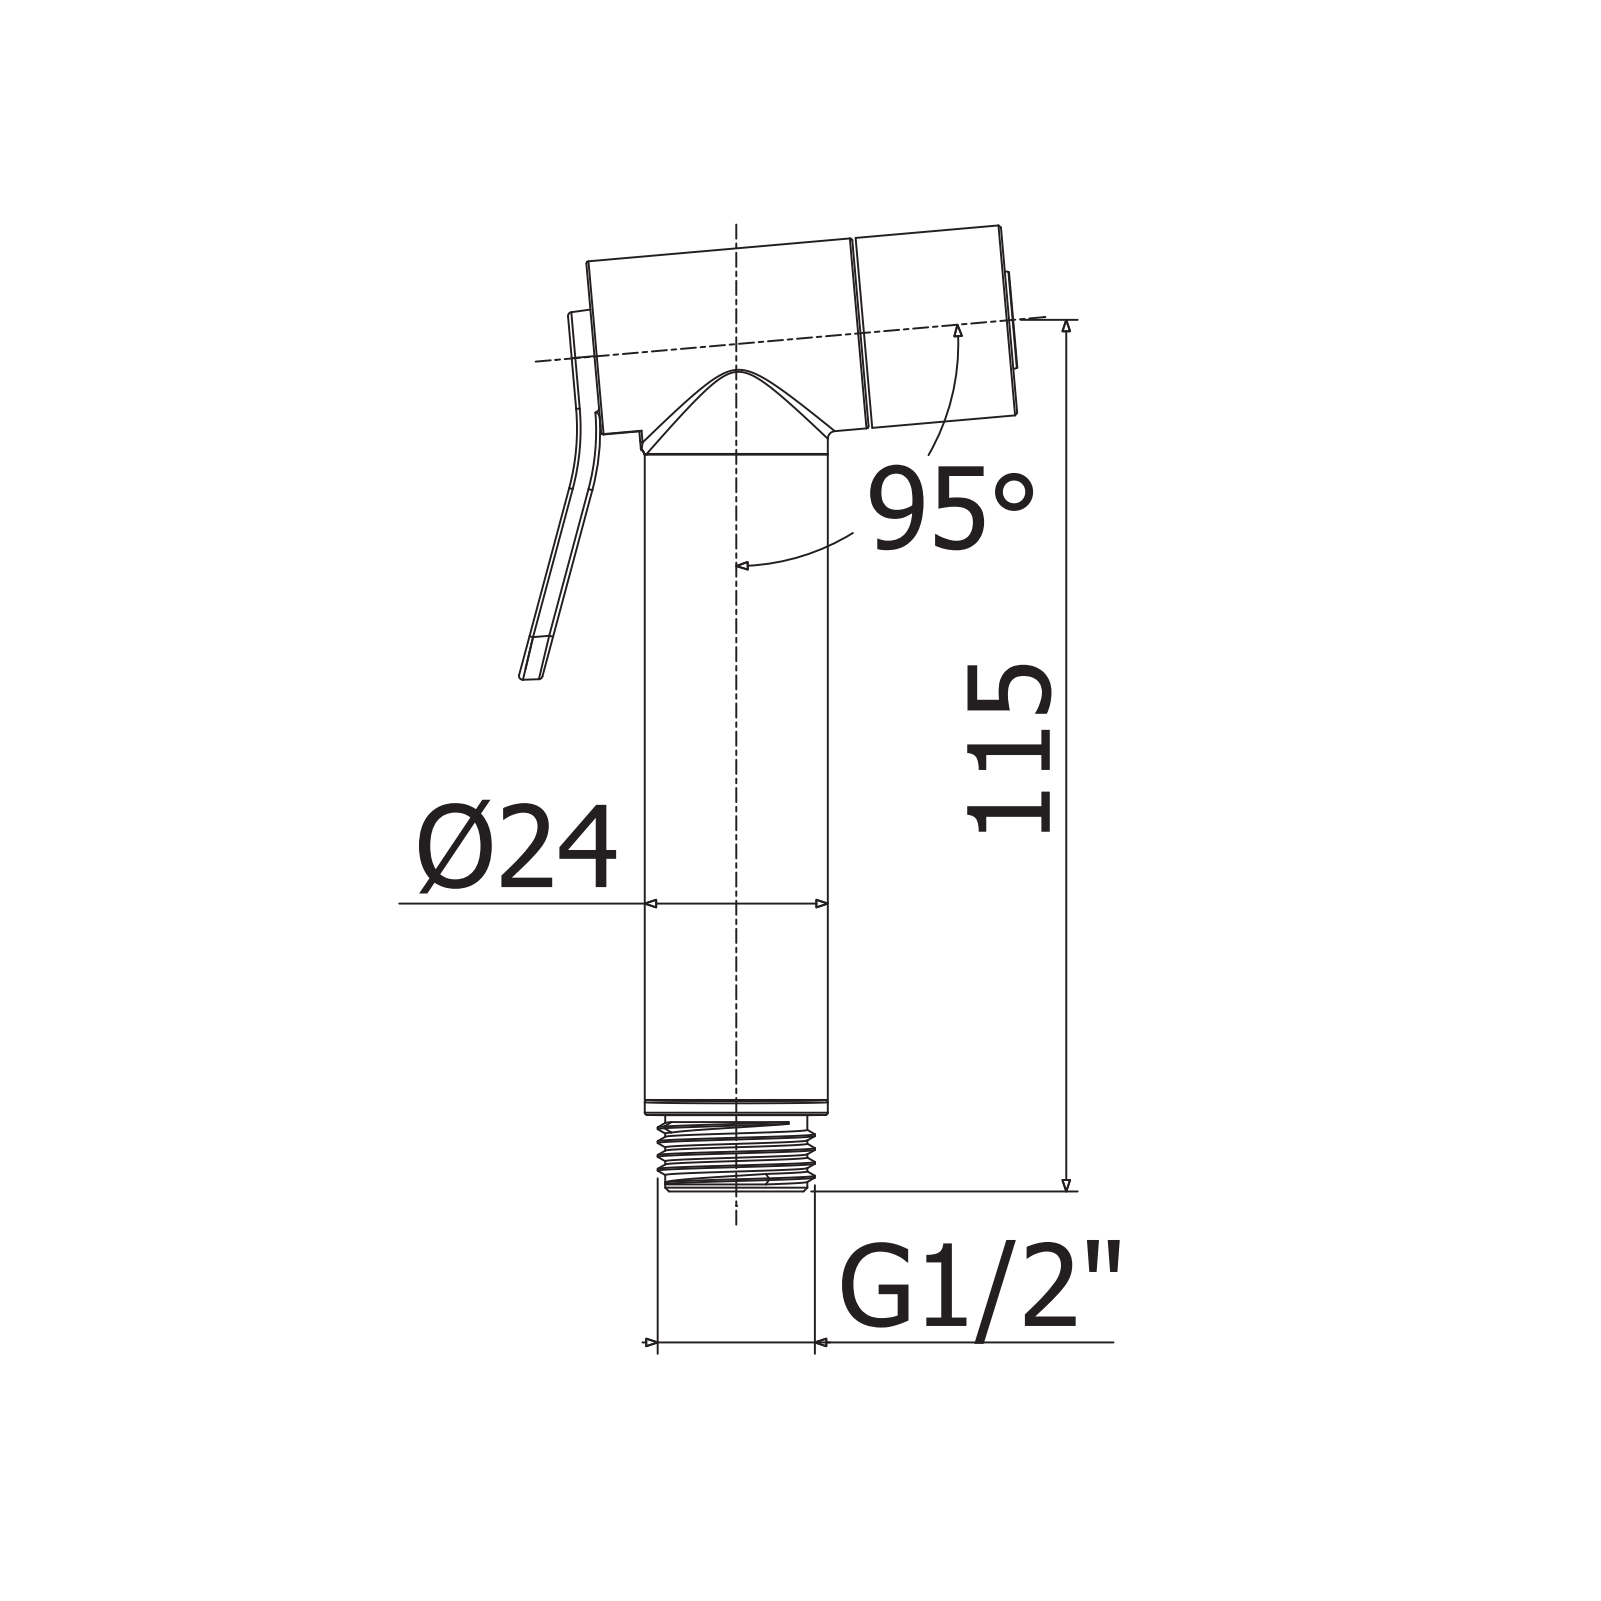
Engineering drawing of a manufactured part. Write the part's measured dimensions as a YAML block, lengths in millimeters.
part_name: "ZDOC126CR"
step_written_by: "CREO PARAMETRIC BY PTC INC, 2022124 (CONFIG_CONTROL_DESIGN)"
units: millimeters
bodies: {solids: 0, faces: 789, planar: 298, cylindrical: 165, other: 326}
overall_size: [126.66, 65.33, 25]
round_holes:
  - {diameter: 16.38, count: 1}
  - {diameter: 23, count: 1}
round_bosses_or_shafts:
  - {diameter: 25, count: 1}
  - {diameter: 24, count: 1}
  - {diameter: 21.9, count: 1}
  - {diameter: 20, count: 1}
  - {diameter: 18.63, count: 1}
partial_cylinders:
  - {radius: 0.1, count: 73}
  - {radius: 0.2, count: 45}
  - {radius: 0.5, count: 6}
  - {radius: 0.3, count: 4}
  - {radius: 30, count: 2}
  - {radius: 6.7, count: 1}
  - {radius: 8.44, count: 1}
face_to_face_distances: [0.46, 19.05, 18.59, 2.99, 35, 35.46, 54.05, 79.4, 7, 28]
